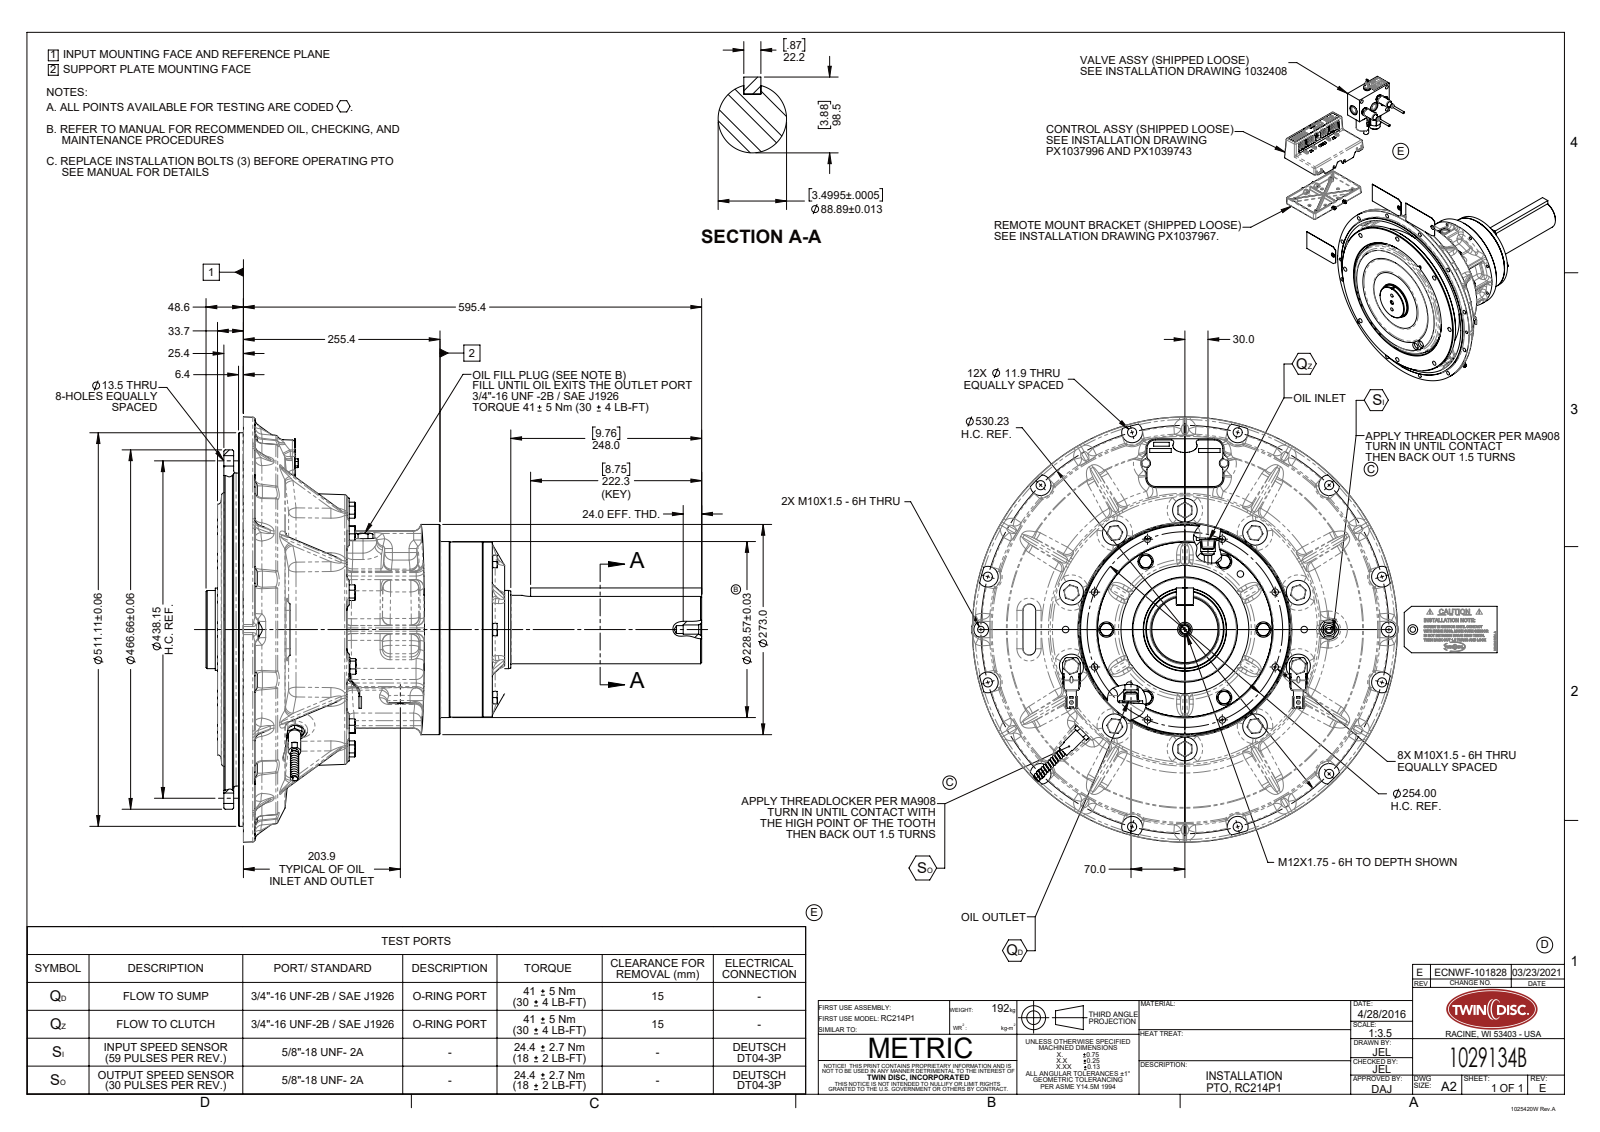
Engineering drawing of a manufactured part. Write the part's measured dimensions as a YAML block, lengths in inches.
part_name: "1029134B"
step_written_by: "SolidWorks 2019 (AUTOMOTIVE_DESIGN)"
units: inches
bodies: {solids: 0, faces: 1822, planar: 414, cylindrical: 366, other: 1042}
overall_size: [25.354, 21.813, 21.744]
round_holes:
  - {diameter: 0.335, count: 14}
  - {diameter: 0.468, count: 10}
  - {diameter: 0.531, count: 8}
  - {diameter: 1.188, count: 3}
  - {diameter: 0.187, count: 2}
  - {diameter: 0.402, count: 2}
  - {diameter: 0.468, count: 2}
  - {diameter: 0.75, count: 2}
  - {diameter: 0.875, count: 2}
  - {diameter: 1, count: 2}
  - {diameter: 0.425, count: 1}
  - {diameter: 0.472, count: 1}
round_bosses_or_shafts:
  - {diameter: 0.625, count: 2}
  - {diameter: 0.315, count: 2}
  - {diameter: 20.123, count: 1}
  - {diameter: 18.373, count: 1}
  - {diameter: 13.658, count: 1}
  - {diameter: 10.866, count: 1}
  - {diameter: 10.748, count: 1}
  - {diameter: 8.999, count: 1}
partial_cylinders:
  - {radius: 0.394, count: 95}
  - {radius: 0.118, count: 74}
  - {radius: 0.197, count: 12}
  - {radius: 0.531, count: 12}
  - {radius: 0.06, count: 8}
  - {radius: 0.045, count: 4}
  - {radius: 0.5, count: 4}
  - {radius: 0.01, count: 3}
face_to_face_distances: [1, 0.528, 0.472, 1.326, 0.798, 0.326, 1.267, 0.739, 0.267, 0.059]
hole_center_spacings: [8.148, 11.506, 4.439, 13.382, 3.827, 5, 6.601, 7.071]
